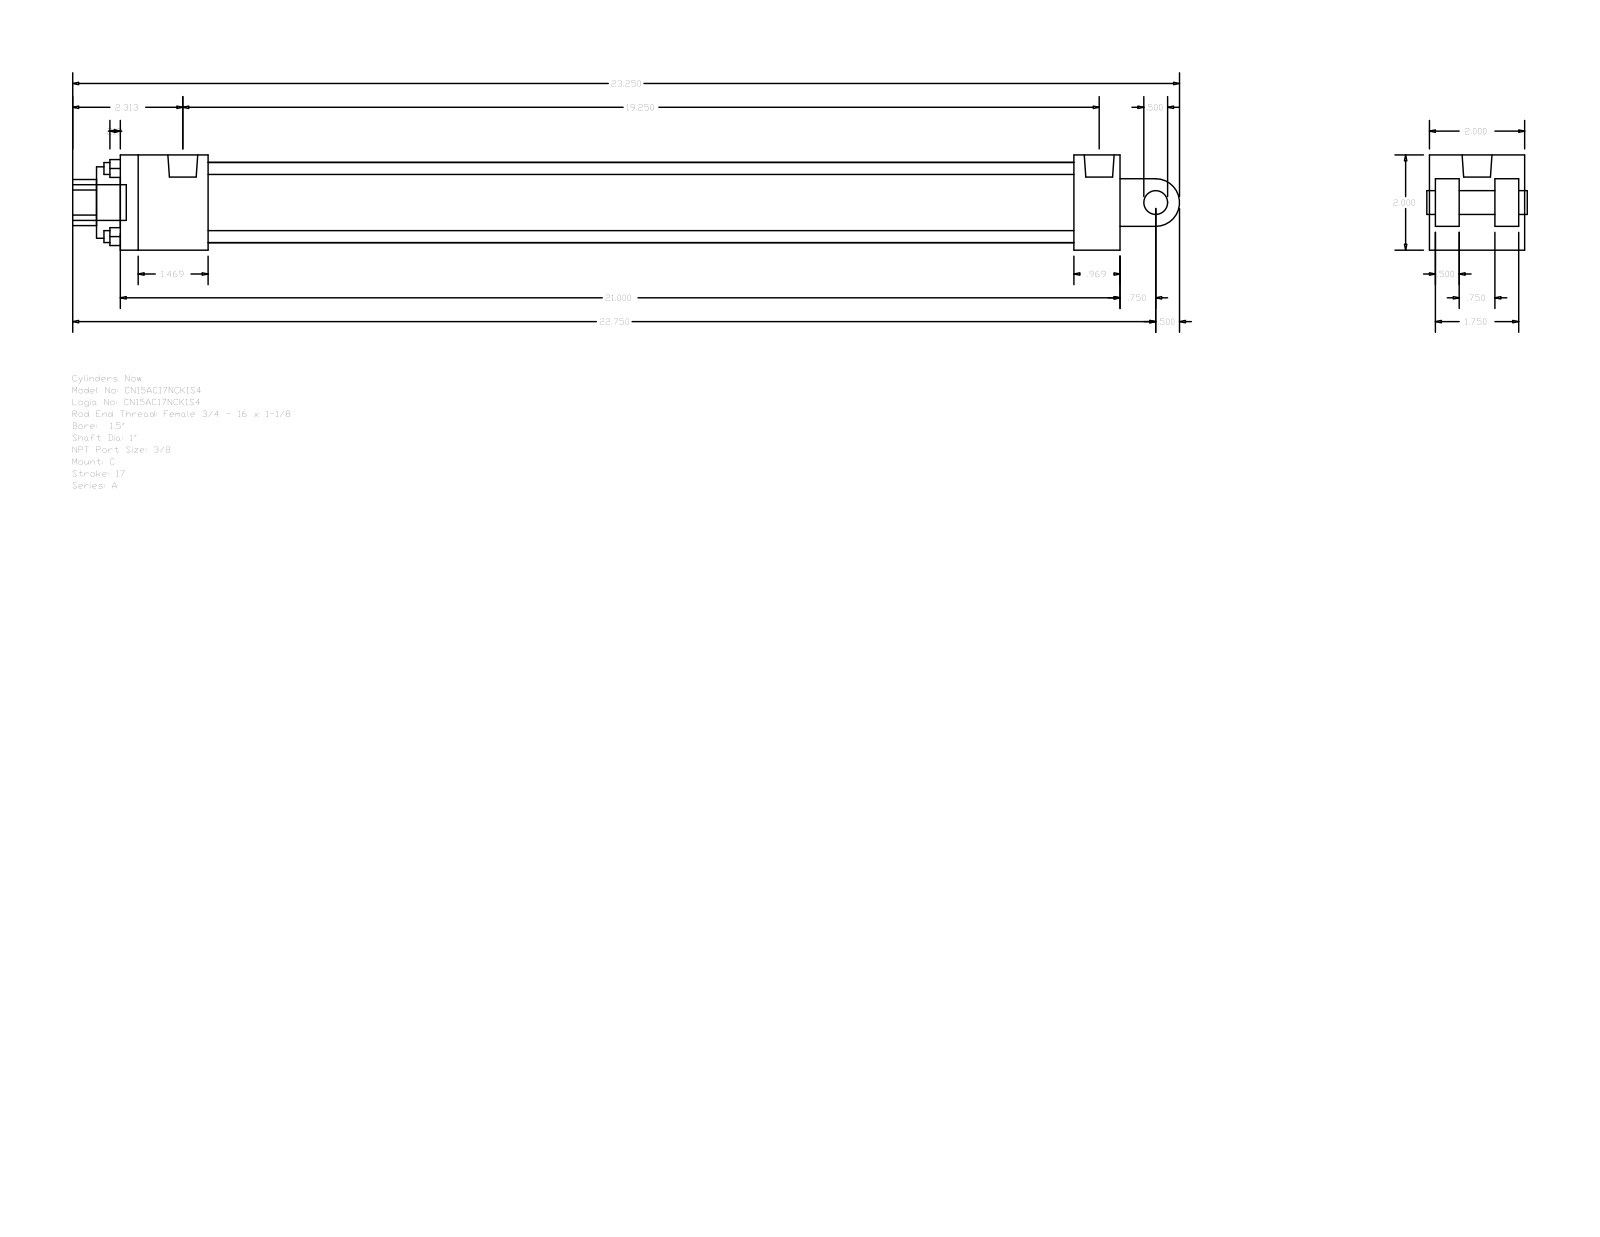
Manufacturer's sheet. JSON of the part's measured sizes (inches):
{"part_name": "A_C__0150_1", "step_written_by": "GSSL Pune (CONFIG_CONTROL_DESIGN)", "units": "inches", "bodies": {"solids": 0, "faces": 99, "planar": 70, "cylindrical": 29, "other": 0}, "overall_size": [23.25, 2, 2], "round_holes": [[0.25, 4], [0.219, 2], [0.627, 1], [1, 1], [1.5, 1], [1.69, 1]], "round_bosses_or_shafts": [[0.219, 2], [0.75, 1], [0.627, 1], [0.5, 1]], "partial_cylinders_radius": [[0.484, 1], [0.5, 1]], "face_to_face_distances": [2, 0.5, 0.125, 0.625, 1.875, 1.375, 1.25, 21, 20.031, 0.969], "hole_center_spacings": [1.011, 1.43, 2.022, 0.156]}
